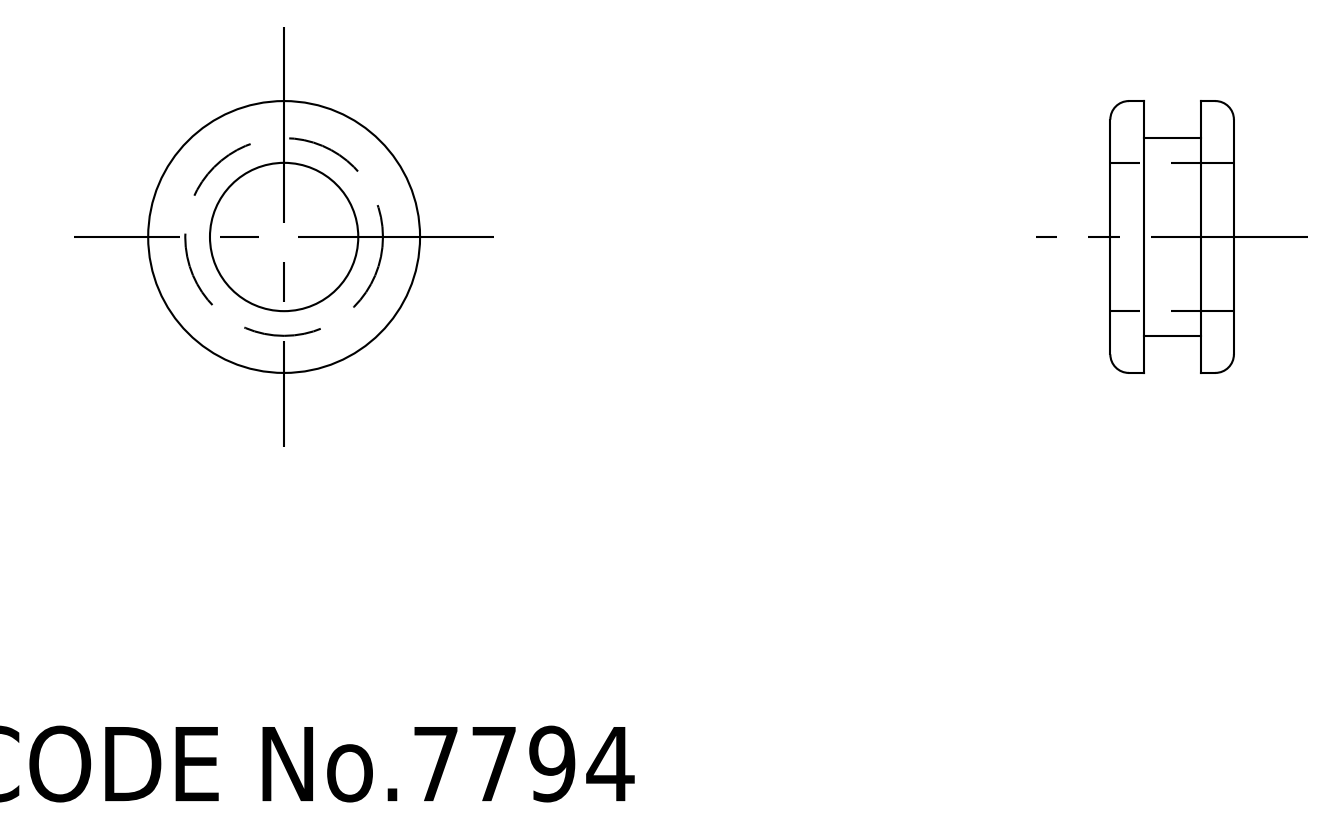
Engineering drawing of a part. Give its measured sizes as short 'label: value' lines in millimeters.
name: TM_346_9
written by: SolidWorks 2015 (AUTOMOTIVE_DESIGN)
unit: mm
bodies: 1 solid, 16 faces (4 planar, 8 cylindrical, 4 other)
size: 11 × 11 × 5
volume: 223 mm³; area: 446 mm²
holes: 1× ⌀6
bosses: 1× ⌀11, 1× ⌀8
face distances: 1.35, 3.65, 2.3, 5
